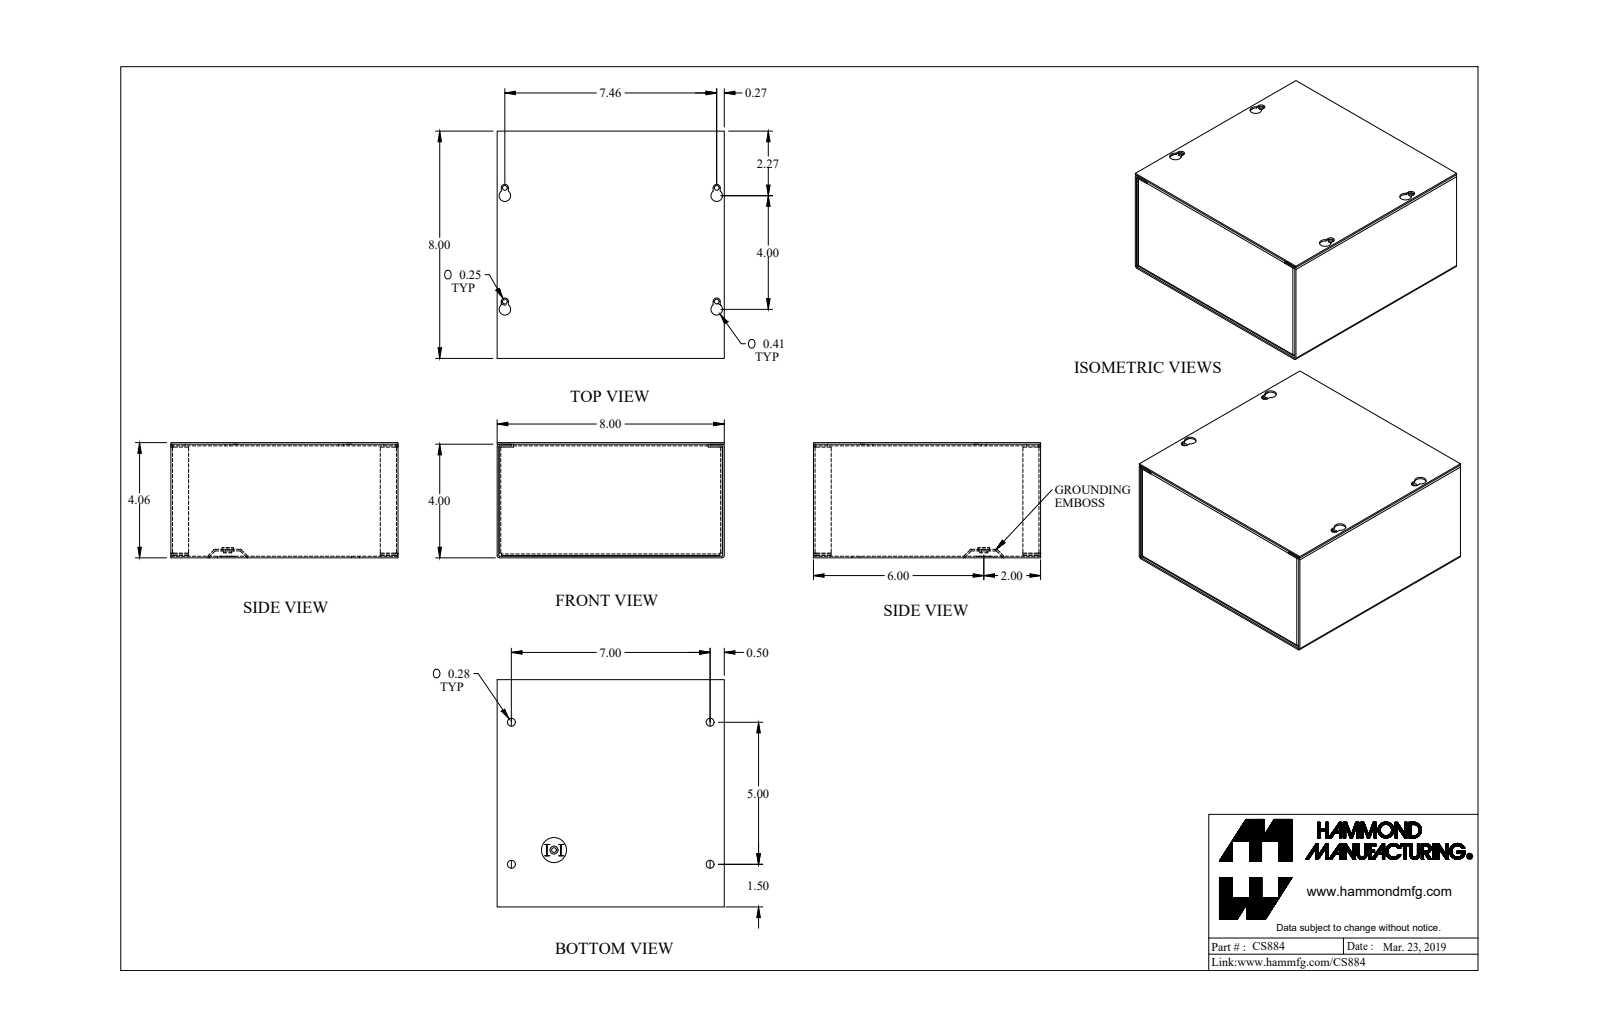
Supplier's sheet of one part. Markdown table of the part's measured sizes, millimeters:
| quantity | value |
| --- | --- |
| part name | CS884_Default |
| STEP written by | SolidWorks 2019 (CONFIG_CONTROL_DESIGN) |
| units | millimeters |
| bodies | 4 solids, 205 faces (125 planar, 72 cylindrical, 8 other) |
| overall size | 203.2 × 203.2 × 103 |
| volume | 261 900 mm³ |
| surface area | 367 400 mm² |
| round holes (diameter × count) | 4.3 × 5, 7.1 × 4, 12.7 × 1 |
| round bosses / shafts (diameter × count) | 12.5 × 1, 7.2 × 1 |
| partial cylindrical surfaces (radius × count) | 0.7 × 12, 2.2 × 12, 1.4 × 8, 3.2 × 4, 5.2 × 4 |
| main face-to-face distances | 1.4, 101.6, 201.8, 100.2, 203.2, 103, 200.3, 2, 98.1, 99.6 |
| hole center spacings | 14, 114.5, 184.1, 216.3, 101.6, 127, 177.8, 189.5 |
